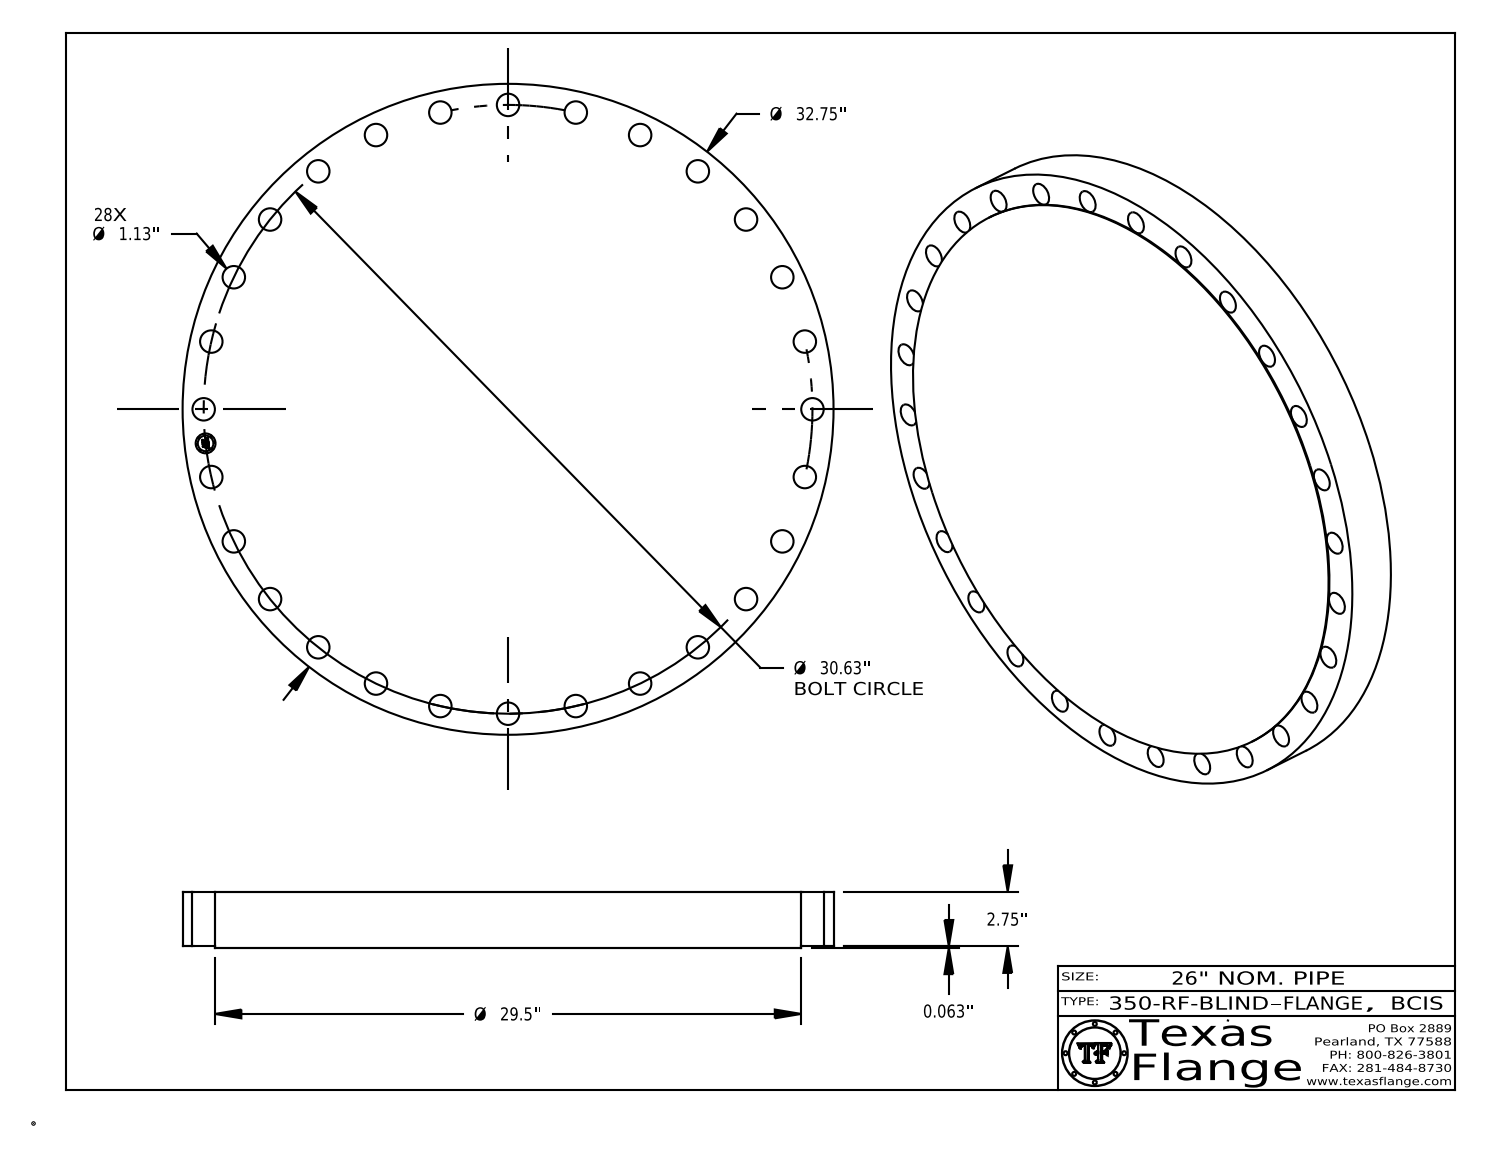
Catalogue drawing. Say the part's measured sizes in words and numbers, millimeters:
The part is named "350-RF-BLIND, Series BCIS". Its 3-D file was written by "CATIA V5 STEP AP214 (AUTOMOTIVE_DESIGN)". It is 1 solid with 448 faces: 368 planar, 80 cylindrical and 0 other. Overall it measures 831.9 by 831.9 by 71.5 millimeters. Its volume is 37 400 000 cubic millimeters and its surface area 1 414 000 square millimeters. Round holes: 28 of diameter 28.7, 1 of diameter 25.4. Round bosses or shafts: 8 of diameter 1.5, 1 of diameter 831.9, 1 of diameter 749.3, 1 of diameter 20. The main face-to-face distances are 71.5, 1.6, 69.9, 0.4, 71.1, 69.5, 7.6, 7.4, 1.4, 4.9. The hole center spacings are 257, 550.1, 758.5, 773.1, 87.1, 413.9, 608.3, 173.1.
